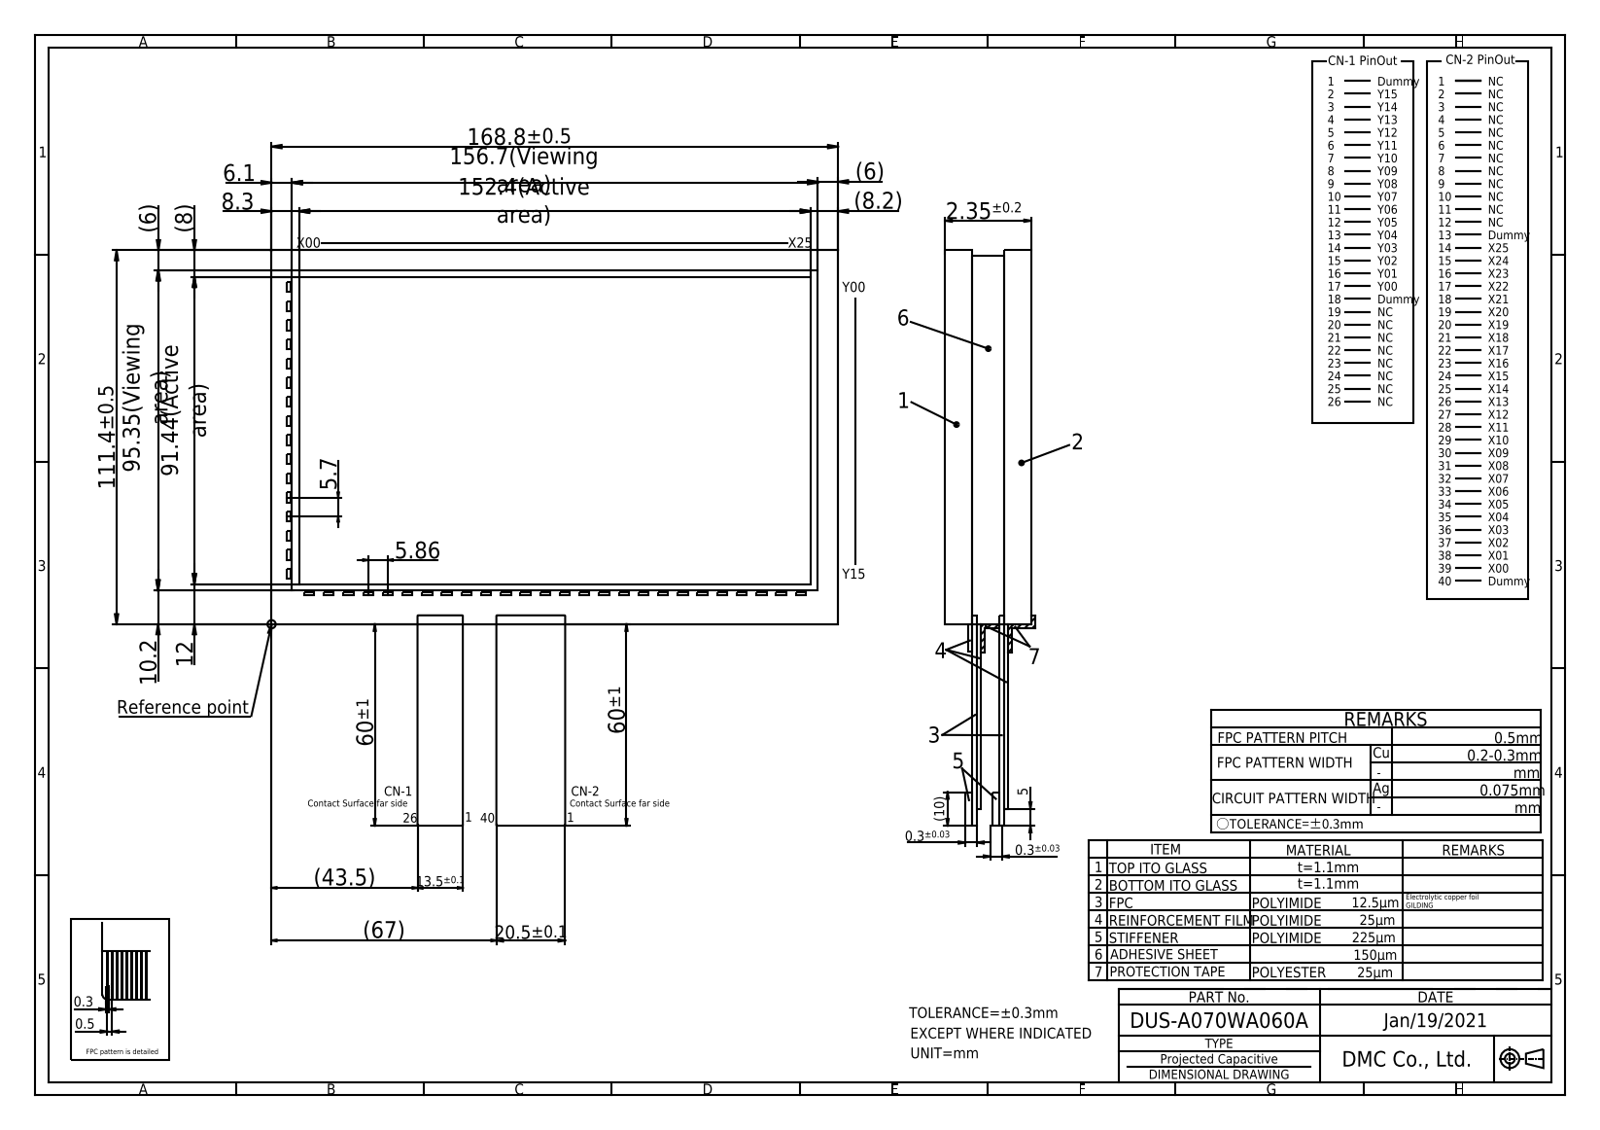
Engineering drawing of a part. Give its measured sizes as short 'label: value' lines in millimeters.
name: DUS-A070WA060A
written by: Autodesk Inventor 2020 (CONFIG_CONTROL_DESIGN)
unit: mm
bodies: 1 solid, 302 faces (298 planar, 4 cylindrical, 0 other)
size: 236.32 × 193.68 × 2.35
volume: 44 398 mm³; area: 43 168 mm²
rounds: 4× R0.2
face distances: 2.35, 1.14, 1.21, 1.25, 1.1, 1.11, 1, 2.25, 111.4, 0.8
